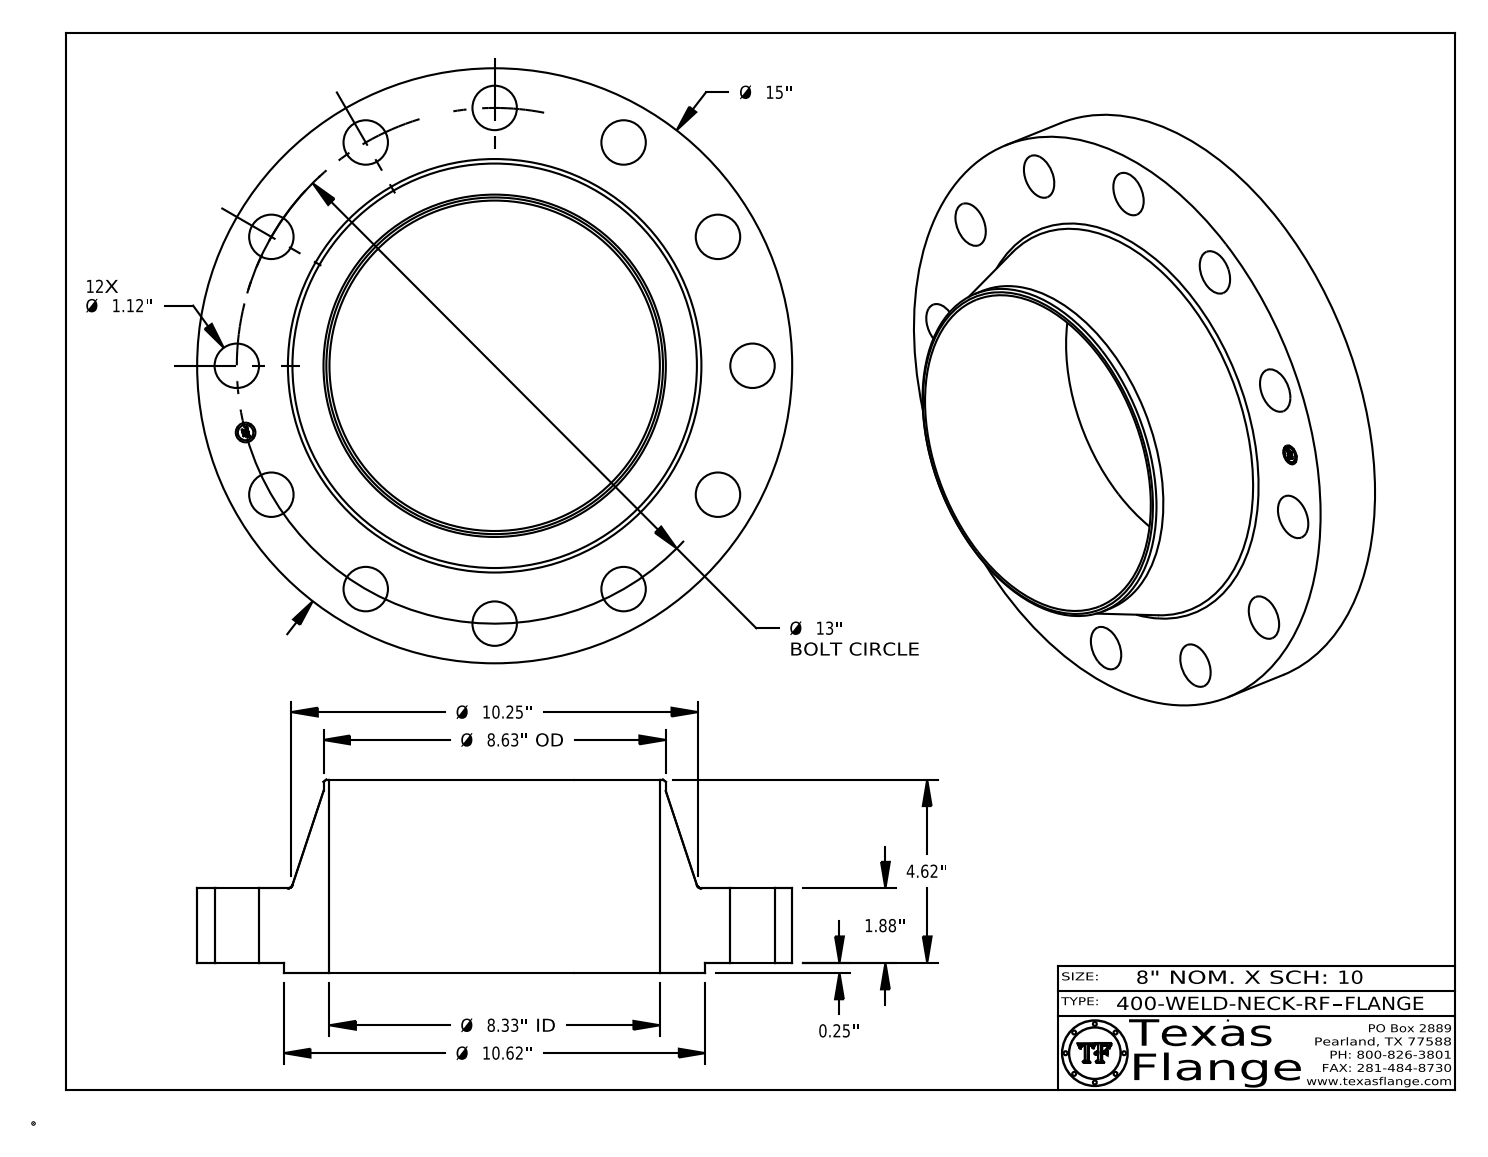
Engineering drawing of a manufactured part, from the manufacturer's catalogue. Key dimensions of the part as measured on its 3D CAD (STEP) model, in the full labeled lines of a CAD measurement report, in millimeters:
Part name (STEP PRODUCT): 400-WELD-NECK-RF
STEP written by: CATIA V5 STEP AP214 (AUTOMOTIVE_DESIGN)
Units: millimetres
Bodies: 1 solid, 427 faces (369 planar, 52 cylindrical, 6 other)
Overall size (bounding box): 381 × 381 × 123.7
Volume: 4 189 000 mm³ · Surface area: 376 300 mm²
Round holes (diameter × count): ⌀28.4 ×12, ⌀12.6 ×1, ⌀211.6 ×1
Round bosses / shafts (diameter × count): ⌀0.8 ×8, ⌀381 ×1, ⌀269.7 ×1, ⌀219.2 ×1, ⌀9.9 ×1
Main face-to-face distances: 47.8, 6.4, 54.1, 123.7, 117.3, 69.6, 53.7, 47.4, 0.4, 70
Hole centre spacings: 165.1, 85.5, 233.5, 286, 318.9, 330.2, 43.1, 126.4
